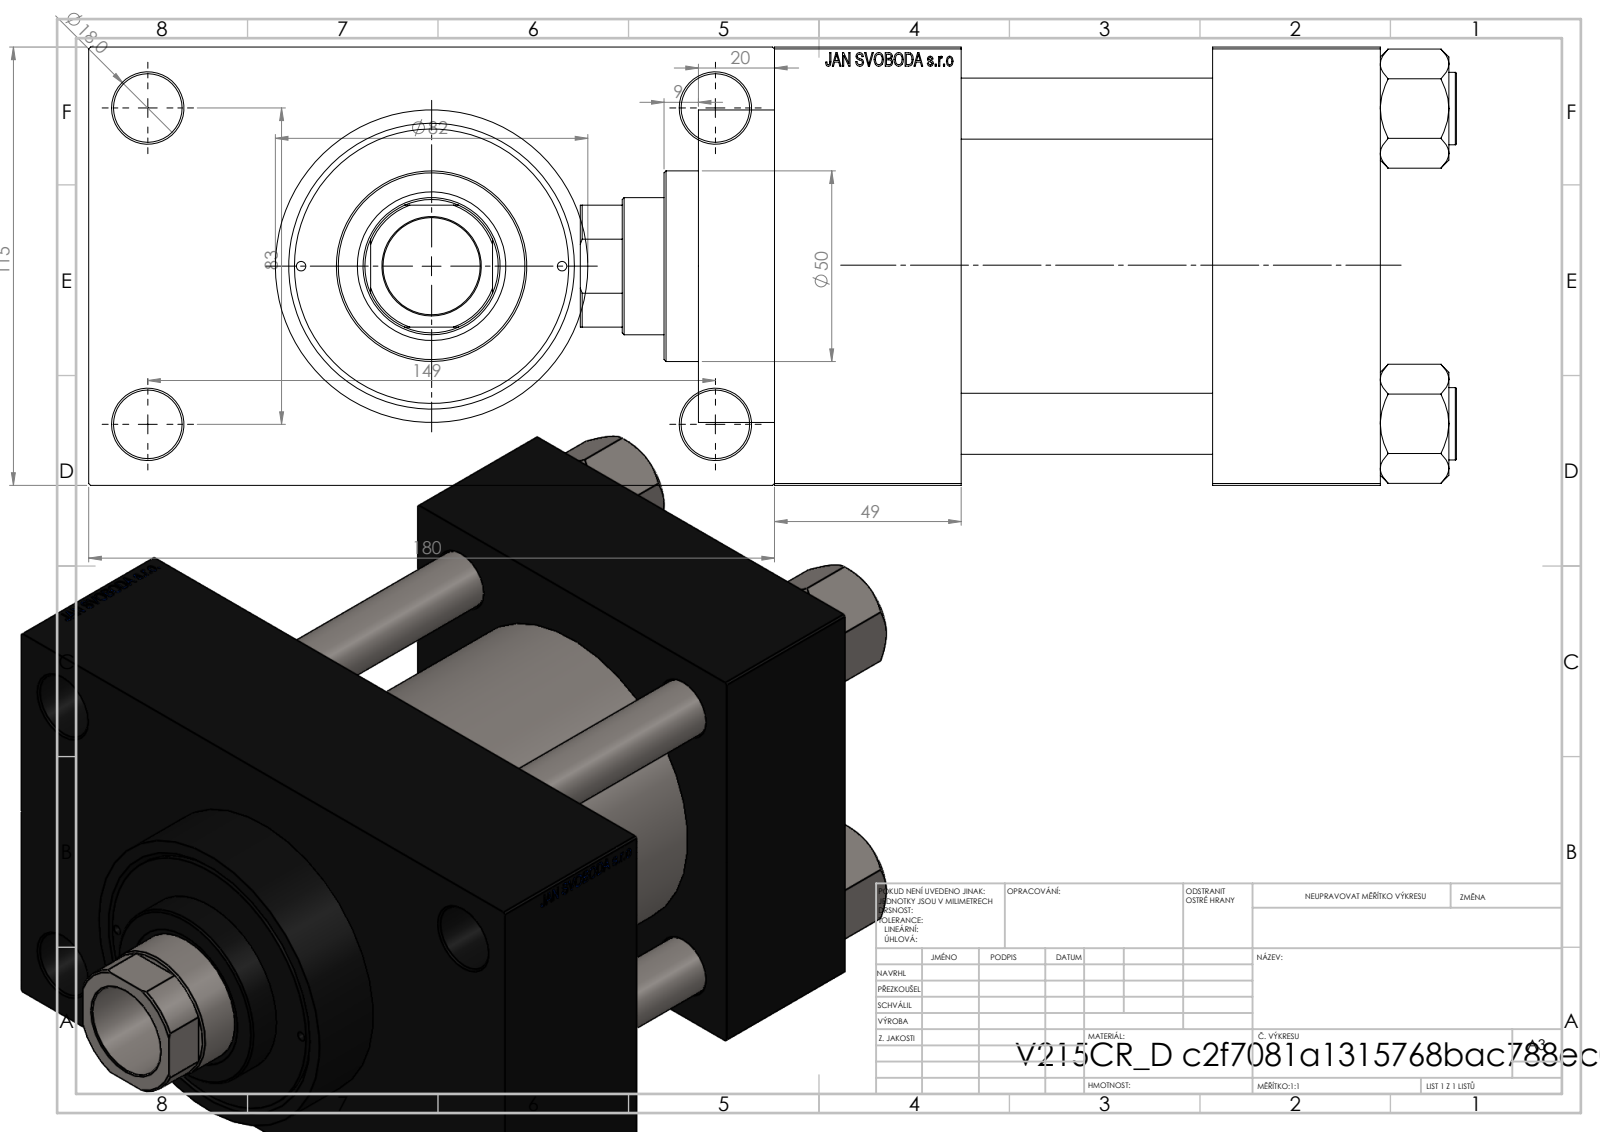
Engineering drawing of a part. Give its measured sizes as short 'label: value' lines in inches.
name: NUT_M5_D; V215CR_D_Body; V215CR_VCP_D; V215CR_D_TYCINKA (+1 more)
written by: SolidWorks 2019 (CONFIG_CONTROL_DESIGN)
unit: in
bodies: 11 solids, 1159 faces (547 planar, 92 cylindrical, 520 other)
size: 9.055 × 7.087 × 4.528
volume: 120.8 in³; area: 459.5 in²
holes: 4× ⌀0.63, 4× ⌀0.709, 2× ⌀0.098, 2× ⌀0.276, 2× ⌀1.041, 2× ⌀1.378, 1× ⌀1.004, 1× ⌀1.417, 1× ⌀1.535, 1× ⌀2.402, 1× ⌀2.835, 1× ⌀3.15
bosses: 4× ⌀0.748, 1× ⌀3.386, 1× ⌀3.228, 1× ⌀1.969
rounds: 1× R0.689
face distances: 4.528, 2.598, 4.331, 1.929, 1.732, 6.26, 1.28, 5.807, 0.787, 2.717
hole spacings: 1.305, 1.652, 2.276, 2.302, 3.256, 3.357, 3.393, 3.513
